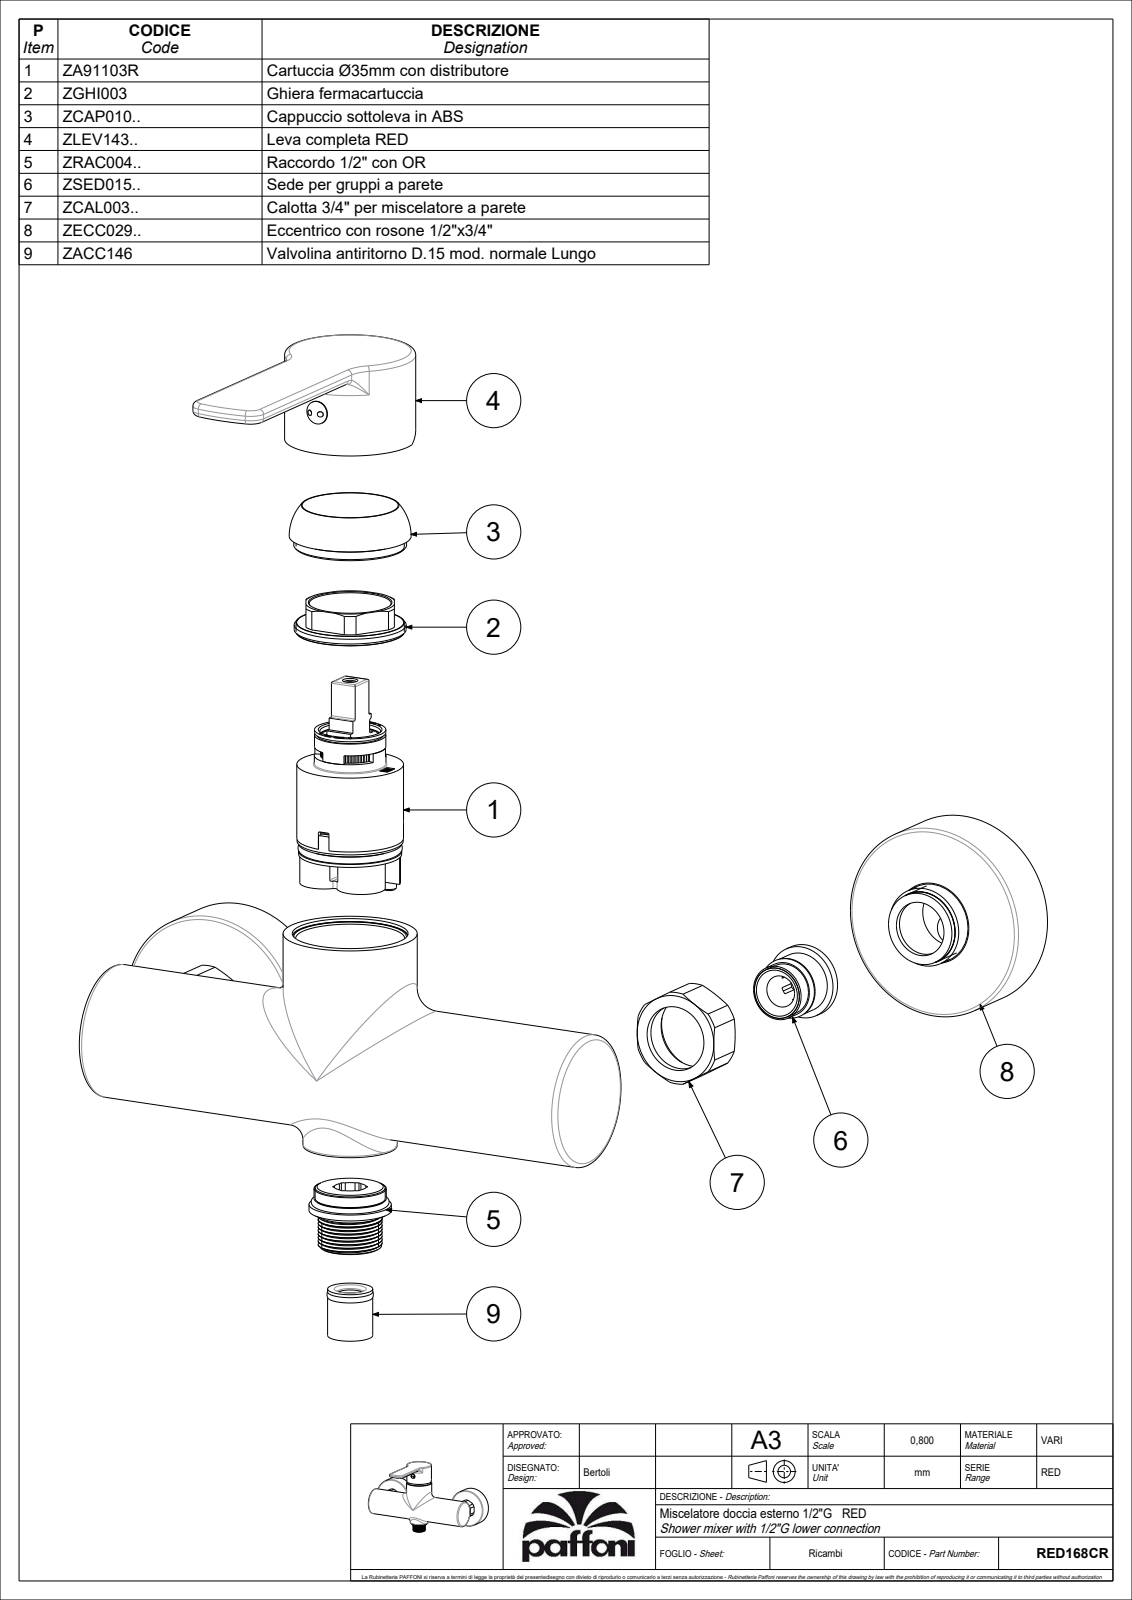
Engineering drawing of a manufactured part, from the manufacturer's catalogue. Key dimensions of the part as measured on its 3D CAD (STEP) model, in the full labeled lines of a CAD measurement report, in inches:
Part name (STEP PRODUCT): RED168CR
STEP written by: CREO PARAMETRIC BY PTC INC, 2020044 (CONFIG_CONTROL_DESIGN)
Units: inches
Bodies: 1 solid, 1511 faces (752 planar, 439 cylindrical, 320 other)
Overall size (bounding box): 8.406 × 5.61 × 4.714
Volume: 12.11 in³ · Surface area: 214.1 in²
Round holes (diameter × count): ⌀0.354 ×3, ⌀0.472 ×3, ⌀0.13 ×2, ⌀0.157 ×2, ⌀0.276 ×2, ⌀0.315 ×2, ⌀0.413 ×2, ⌀0.709 ×2, ⌀0.807 ×2, ⌀0.846 ×2, ⌀0.949 ×2, ⌀0.984 ×2
Round bosses / shafts (diameter × count): ⌀1.063 ×3, ⌀2.5 ×2, ⌀1.732 ×2, ⌀0.945 ×2, ⌀0.776 ×2, ⌀0.354 ×2, ⌀1.693 ×1, ⌀1.378 ×1
Partial cylindrical surfaces — rounded edges, fillets, slot ends (radius × count): R0.02 ×83, R0.006 ×11, R0.012 ×9, R0.039 ×4, R0.059 ×4, R0.276 ×4, R0.394 ×3, R0.197 ×2
Main face-to-face distances: 0.024, 1.083, 2.697, 4.429, 0.128, 6.998, 2.569, 4.301, 0.177, 0.354
Hole centre spacings: 0.028, 0.335, 0.339, 0.513, 0.52, 0.532, 3.538, 3.831
